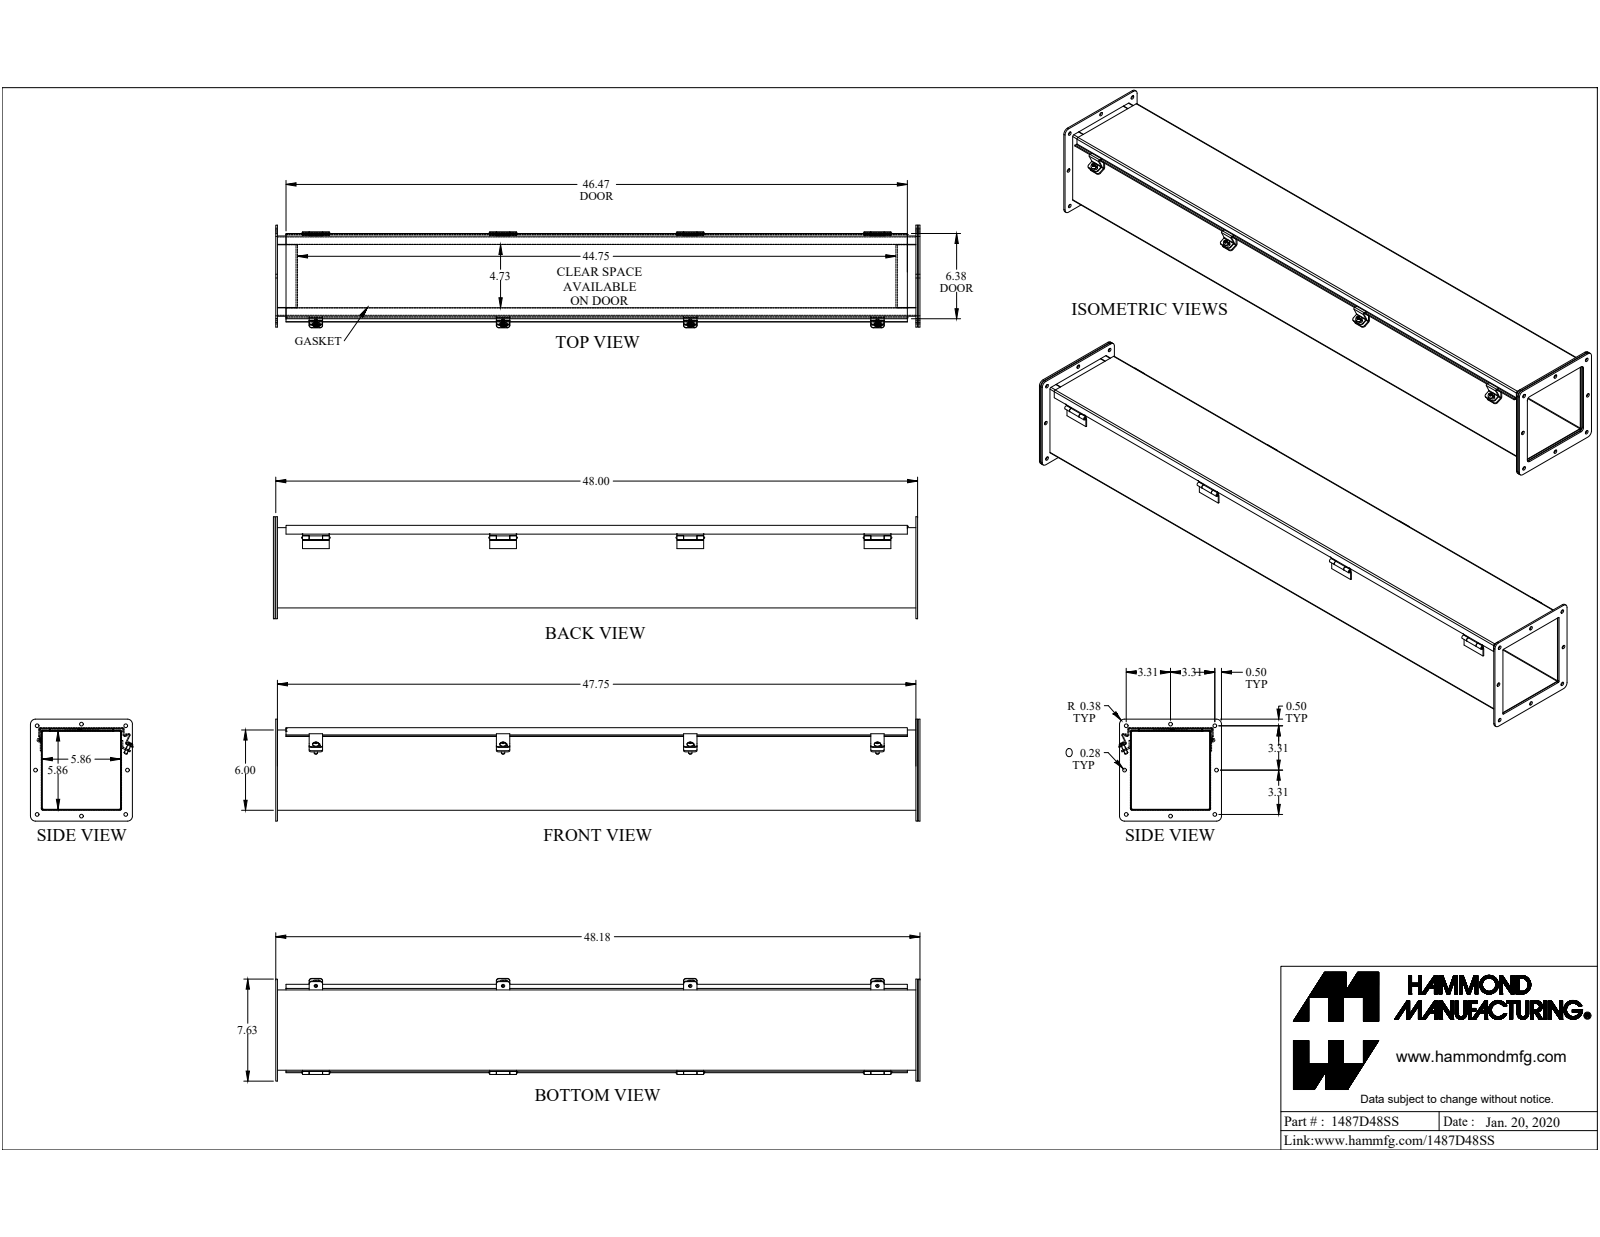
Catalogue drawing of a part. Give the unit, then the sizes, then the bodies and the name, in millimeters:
Units: millimetres
Overall size (bounding box): 1233.1 × 195 × 193.7
Round holes (diameter × count): ⌀7.1 ×8, ⌀5.4 ×4, ⌀4.7 ×1, ⌀5 ×1, ⌀6.6 ×1, ⌀8.9 ×1
Round bosses / shafts (diameter × count): ⌀6.4 ×5, ⌀12.2 ×4, ⌀12.7 ×1, ⌀8.6 ×1, ⌀4.6 ×1
Partial cylindrical surfaces — rounded edges, fillets, slot ends (radius × count): R4.8 ×16, R0.8 ×8, R3.6 ×8, R9.5 ×8, R0.9 ×7, R2.7 ×7, R0.5 ×6, R1.6 ×4
Main face-to-face distances: 1.8, 150.6, 154.9, 152.4, 148.7, 156.8, 153.1, 4.7, 4.4, 6.6
Hole centre spacings: 191, 84.2, 355.6, 84.2, 123.5, 123.5, 168.3, 168.3
Volume: 1 919 000 mm³ · Surface area: 1 939 000 mm²
Bodies: 39 solids, 794 faces (508 planar, 216 cylindrical, 70 other)
Part name (STEP PRODUCT): 1487D48SS
STEP written by: SolidWorks 2019 (CONFIG_CONTROL_DESIGN)
